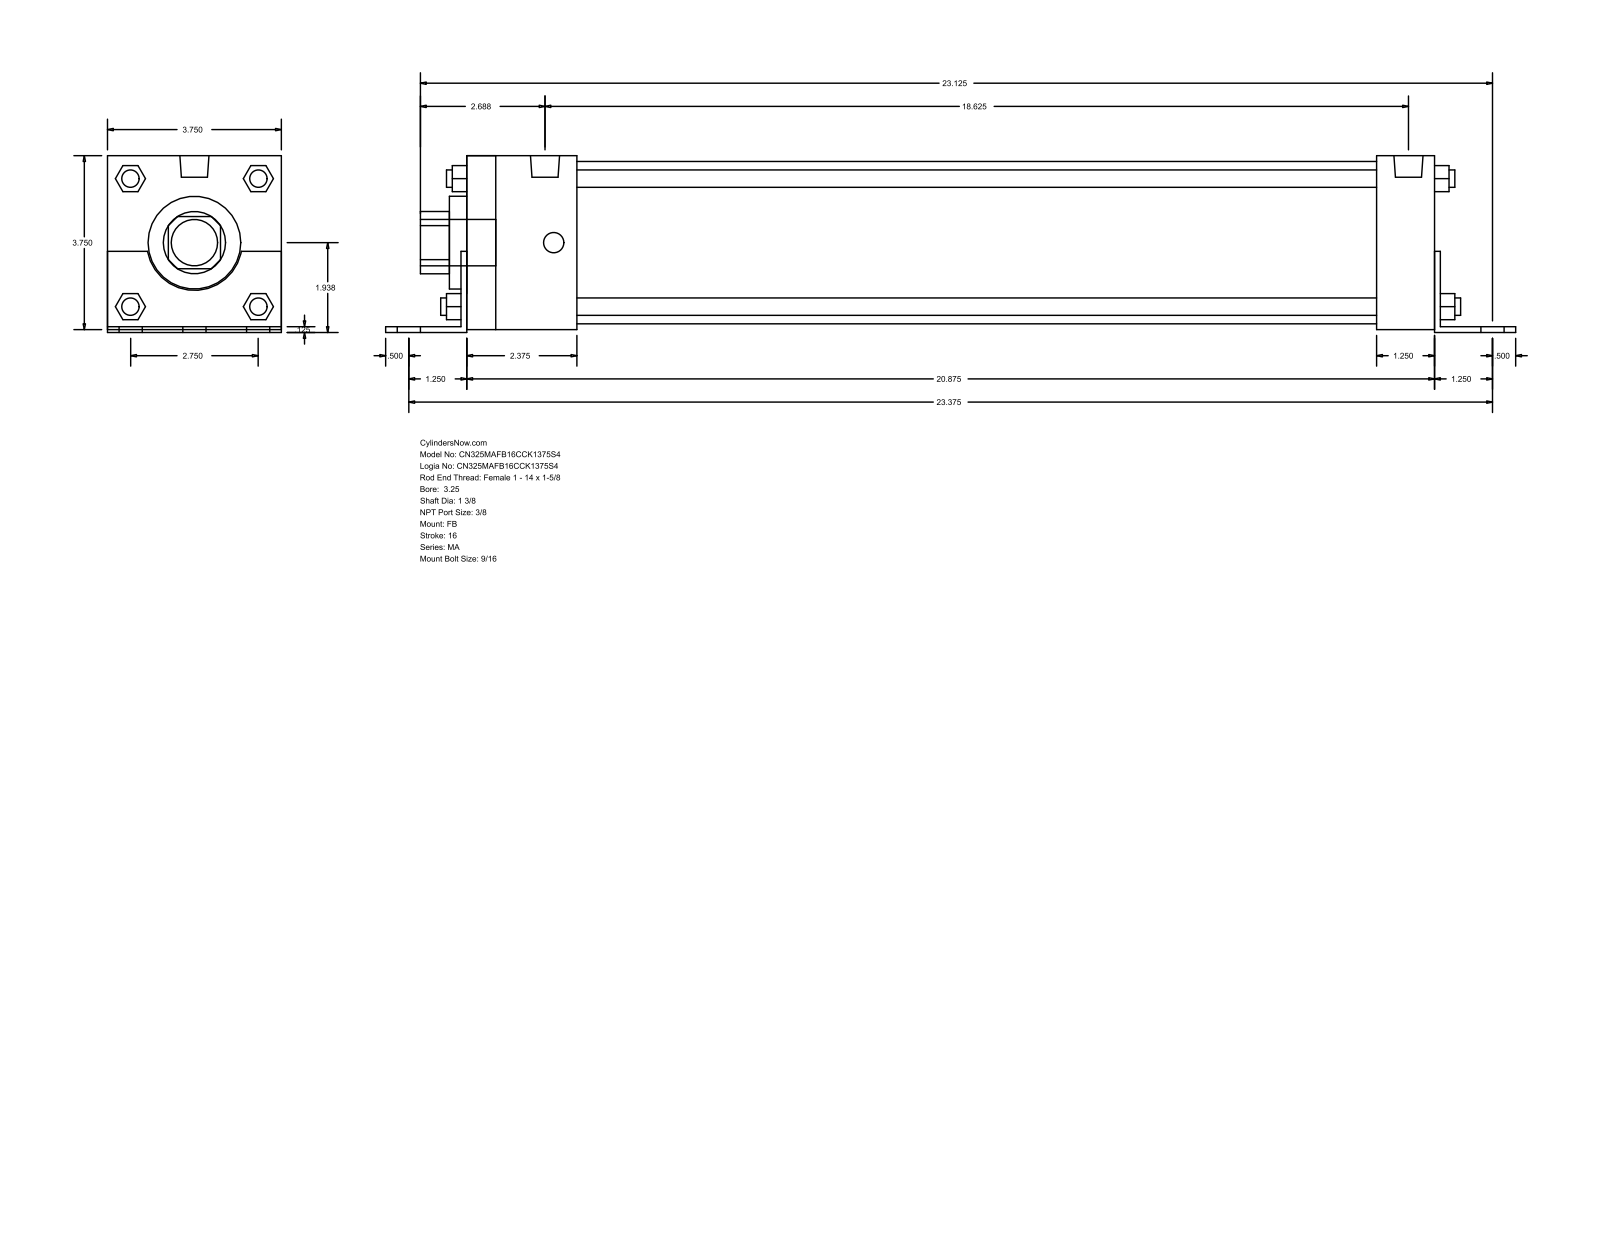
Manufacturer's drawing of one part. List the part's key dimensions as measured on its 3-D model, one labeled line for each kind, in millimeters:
Part name (STEP PRODUCT): MA_FB__0325_1.375
STEP written by: GSSL Pune (CONFIG_CONTROL_DESIGN)
Units: millimetres
Bodies: 0 solids, 140 faces (105 planar, 35 cylindrical, 0 other)
Overall size (bounding box): 619.12 × 96.84 × 95.25
Round holes (diameter × count): ⌀34.92 ×1, ⌀50.8 ×1, ⌀88.9 ×1
Round bosses / shafts (diameter × count): ⌀14.29 ×6, ⌀11.11 ×4, ⌀9.53 ×4, ⌀15.93 ×2, ⌀25.4 ×1
Partial cylindrical surfaces — rounded edges, fillets, slot ends (radius × count): R17.06 ×1, R26.16 ×1
Main face-to-face distances: 95.24, 3.17, 1.59, 96.83, 1.58, 93.66, 3.18, 530.22, 533.4, 60.32
